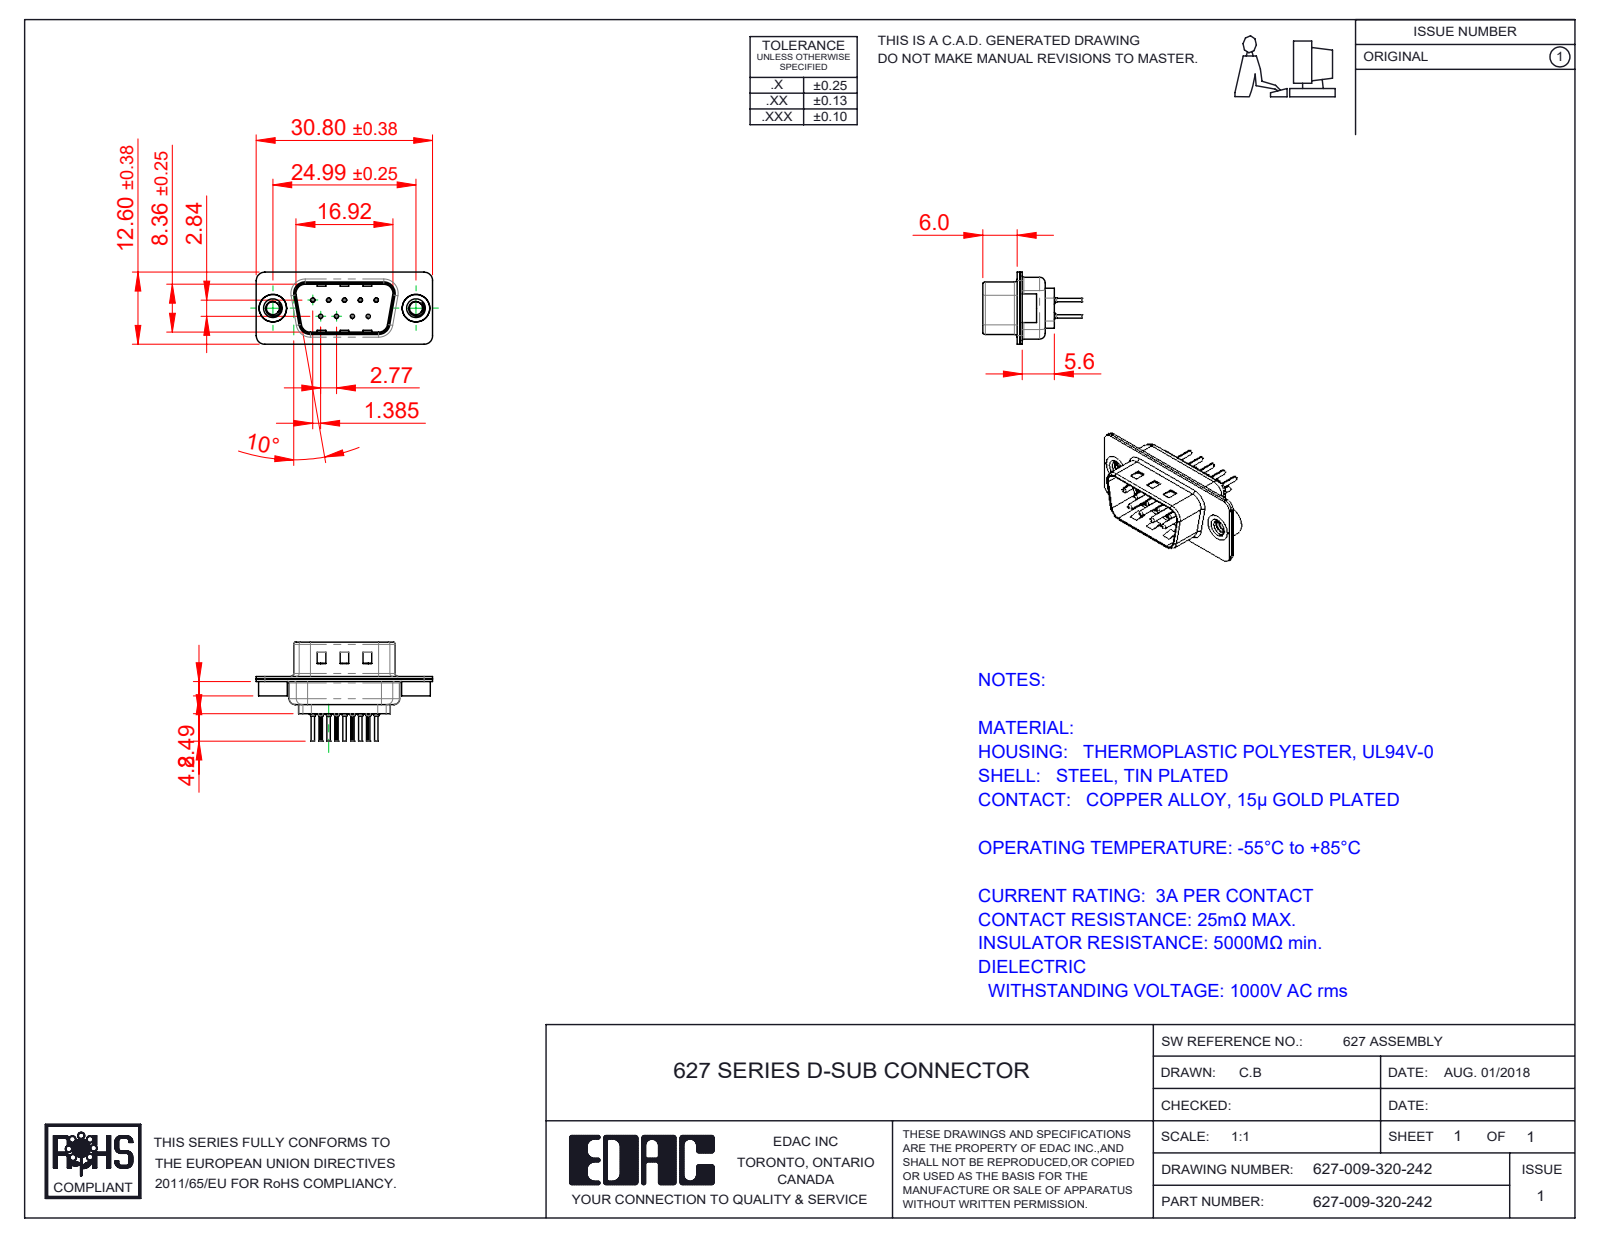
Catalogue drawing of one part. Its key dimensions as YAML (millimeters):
part_name: "627 Shell Front_09 Contacts; 627-009-320-042; 627 Contact Row 1_20L; 627 Housing_09 LP (+3 more)"
step_written_by: "SolidWorks 2020 (CONFIG_CONTROL_DESIGN)"
units: millimeters
bodies: {solids: 14, faces: 1182, planar: 323, cylindrical: 460, other: 399}
overall_size: [30.8, 17.3, 12.6]
volume: 1307
surface_area: 3924
round_holes:
  - {diameter: 0.2, count: 9}
  - {diameter: 0.35, count: 9}
  - {diameter: 1.1, count: 9}
  - {diameter: 1.6, count: 9}
  - {diameter: 2.26, count: 2}
  - {diameter: 4, count: 2}
  - {diameter: 4.8, count: 2}
round_bosses_or_shafts:
  - {diameter: 2, count: 9}
  - {diameter: 1.5, count: 9}
  - {diameter: 0.75, count: 9}
  - {diameter: 0.6, count: 9}
  - {diameter: 5, count: 2}
  - {diameter: 4.9, count: 2}
partial_cylinders:
  - {radius: 0.1, count: 18}
  - {radius: 1.5, count: 18}
  - {radius: 2, count: 12}
  - {radius: 0.5, count: 8}
  - {radius: 1.6, count: 8}
  - {radius: 0.25, count: 4}
  - {radius: 0.6, count: 4}
  - {radius: 0.65, count: 4}
face_to_face_distances: [0.45, 0.4, 0.9, 0.82, 9.58, 1.4, 8.76, 0.5, 1.5, 5.6]
hole_center_spacings: [3.16, 2.77, 5.54, 5.03, 5.04, 8.31, 7.48, 7.49]
